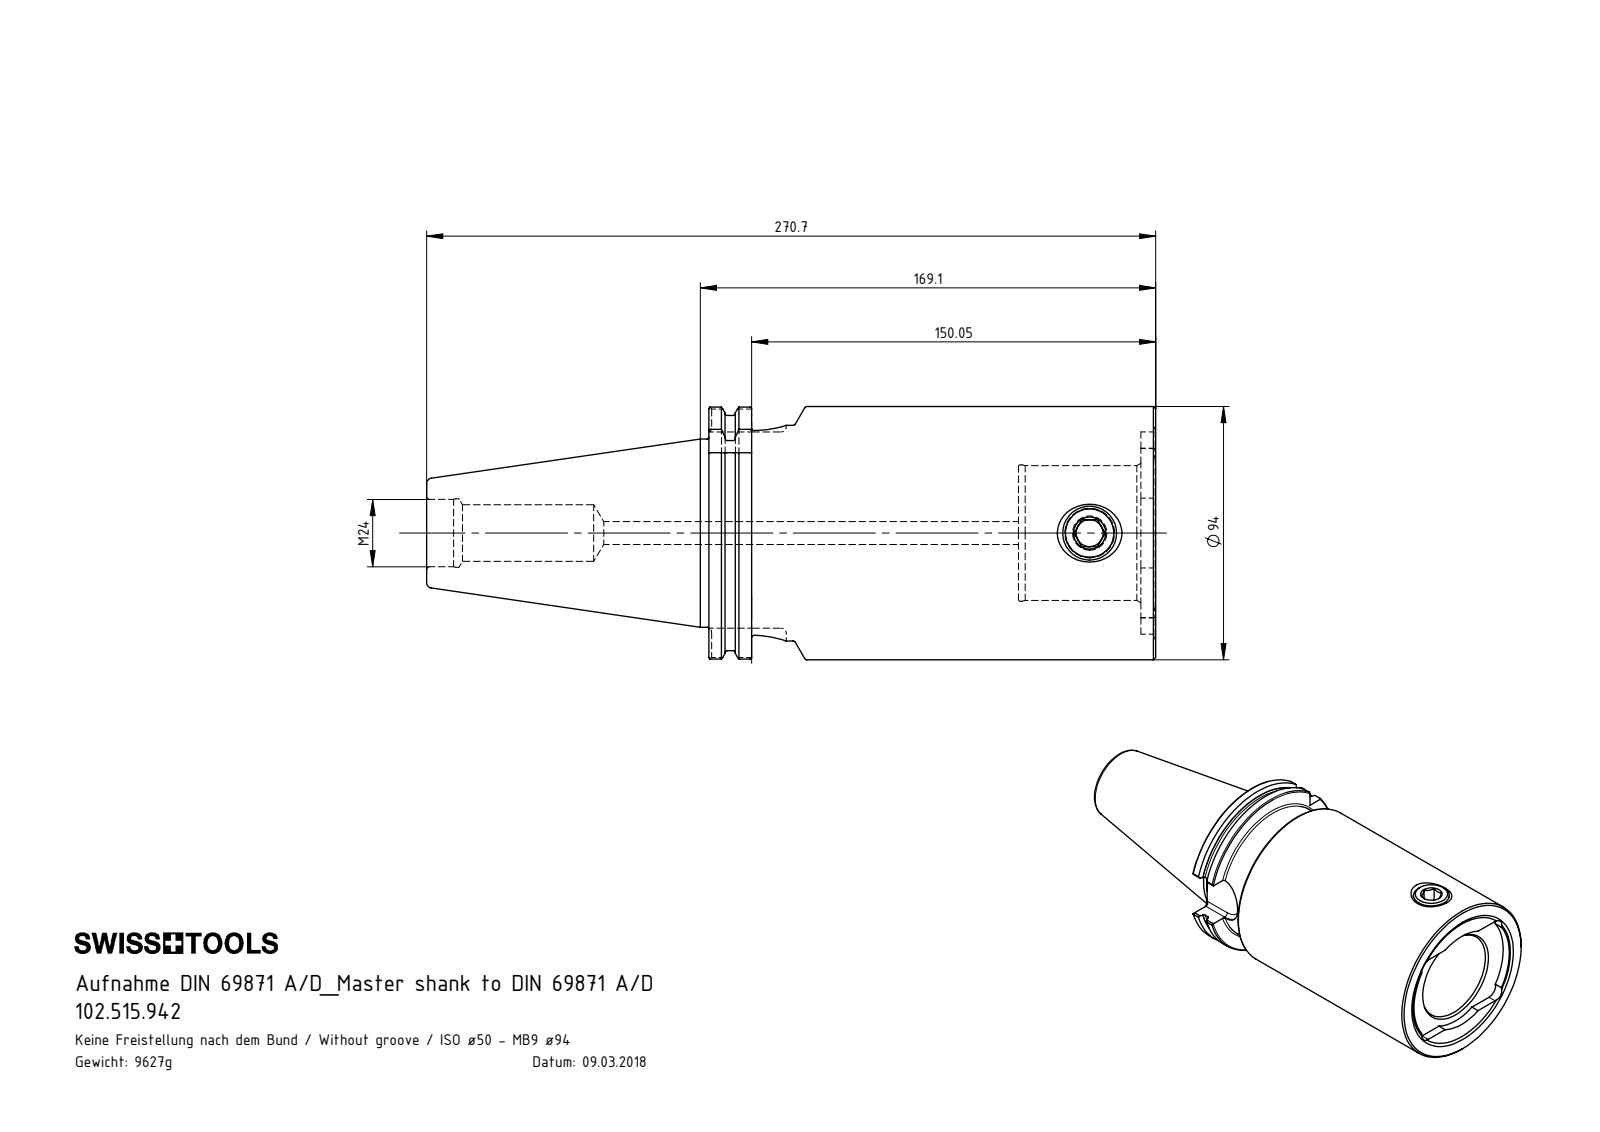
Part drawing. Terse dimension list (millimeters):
name: 102.515.942; MB9-ER1.001.032_A; SK5-MB9.K01.169_C
written by: SolidWorks 2017 (CONFIG_CONTROL_DESIGN)
unit: mm
bodies: 2 solids, 185 faces (56 planar, 56 cylindrical, 73 other)
size: 270.7 × 97.45 × 94
volume: 1 226 000 mm³; area: 101 775 mm²
holes: 1× ⌀8.5, 1× ⌀10, 1× ⌀18.5, 1× ⌀21, 1× ⌀25, 1× ⌀25.45, 1× ⌀50, 1× ⌀50.6
bosses: 1× ⌀94, 1× ⌀91, 1× ⌀80, 1× ⌀69.85, 1× ⌀20
rounds: 8× R2, 4× R5.2, 1× R12.85, 1× R30, 1× R37.52, 1× R48.73
face distances: 114.9, 160.35, 45.45, 165.9, 51, 5.55, 15.85, 99.05, 144.5, 150.05
